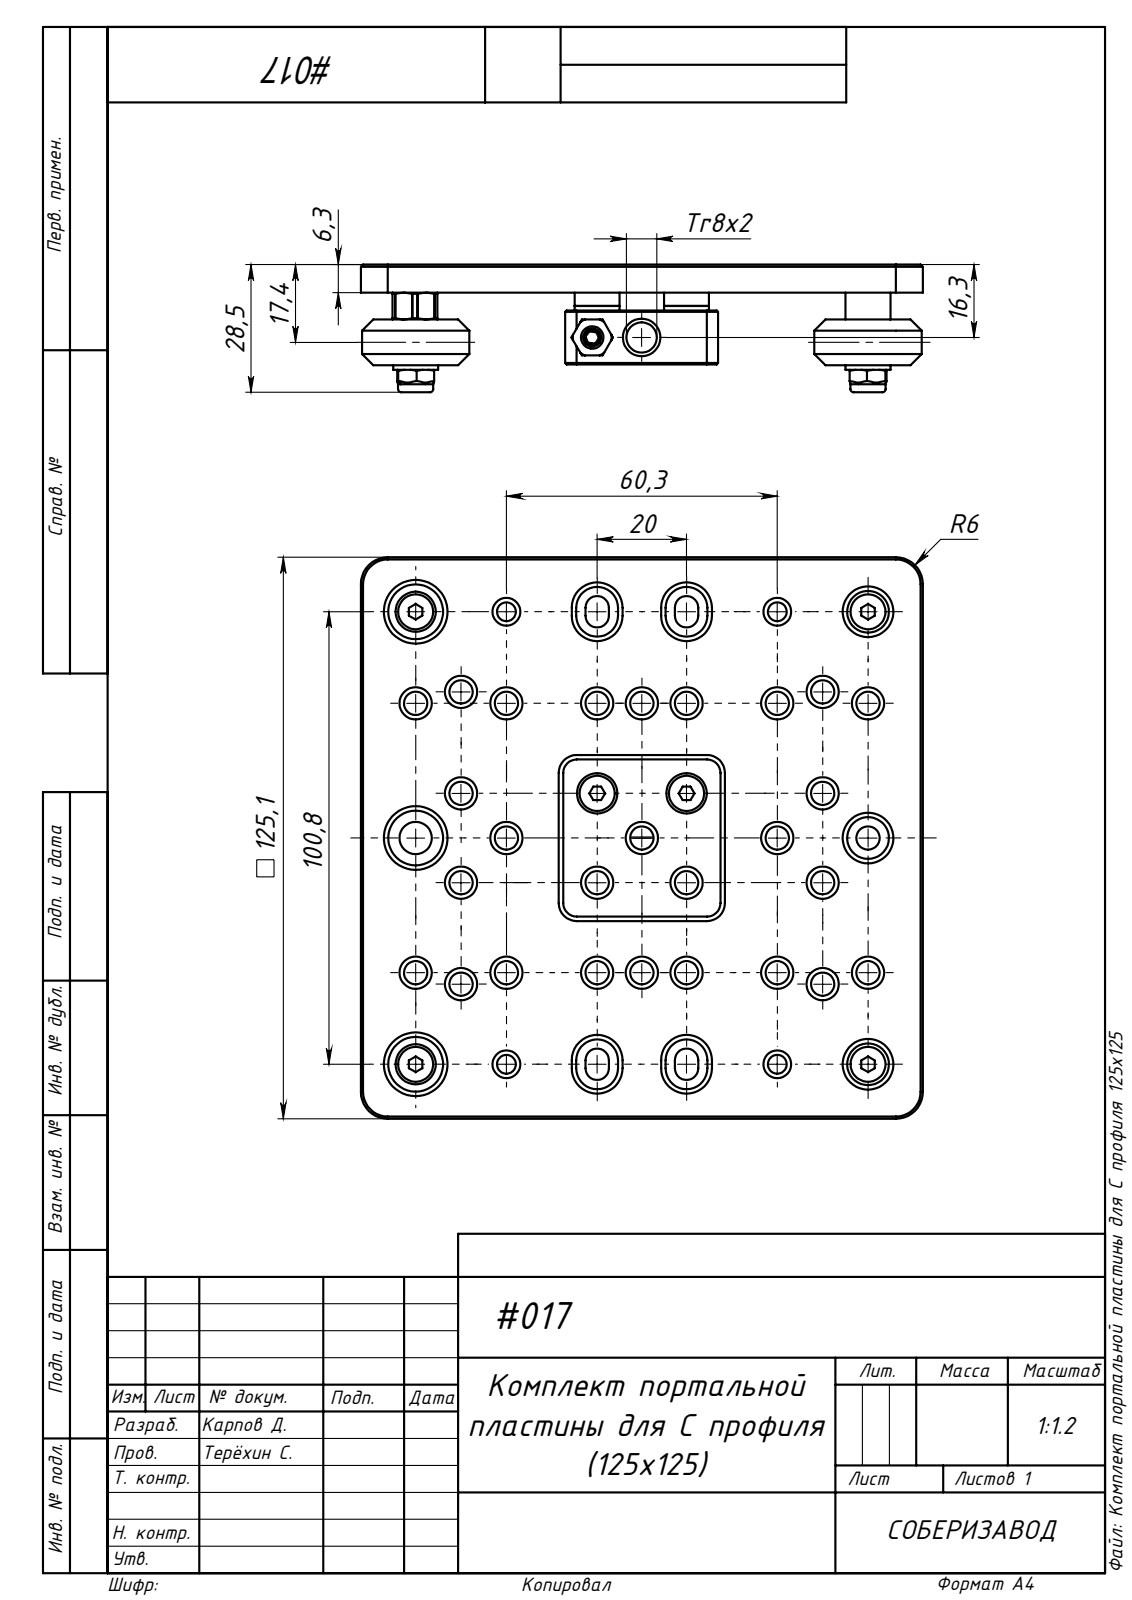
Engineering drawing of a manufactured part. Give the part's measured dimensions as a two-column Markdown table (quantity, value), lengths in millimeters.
| quantity | value |
| --- | --- |
| part name | Гайка М5, низкая DIN 439, K32_00; A211 Высокоточная дистанционная шайба 5 мм_00; A195-Standartnyy-ekstsentrik-6-mm_-dlya-vinta-M5_podrobnaya-model__00; A180 Подшипник 625rs, O 5 O 16 (+7 more) |
| STEP written by | SolidWorks 2021 (AUTOMOTIVE_DESIGN) |
| units | millimeters |
| bodies | 42 solids, 1135 faces (342 planar, 424 cylindrical, 369 other) |
| overall size | 125.1 × 125.1 × 28.45 |
| volume | 118 795 mm³ |
| surface area | 62 478 mm² |
| round holes (diameter × count) | 5.2 × 34, 5 × 6, 5.15 × 6, 4.2 × 5, 4.13 × 4, 13.8 × 4, 14 × 4, 16 × 4, 7.2 × 3, 9.3 × 3, 12.2 × 3, 9.5 × 2 |
| round bosses / shafts (diameter × count) | 10 × 6, 23.9 × 4, 8.95 × 4, 8.6 × 4, 7.83 × 4, 9 × 2, 7 × 2, 5 × 2 |
| partial cylindrical surfaces (radius × count) | 0.2 × 28, 1 × 12, 2.6 × 8, 4.65 × 8, 0.3 × 6, 2.5 × 5, 3 × 4, 6 × 4 |
| main face-to-face distances | 6.25, 2, 4.25, 10.25, 5.2, 5, 0.35, 4.65, 6, 125.1 |
| hole center spacings | 80.5, 14.18, 20.2, 19.9, 36.17, 28.71, 30, 34.08 |
